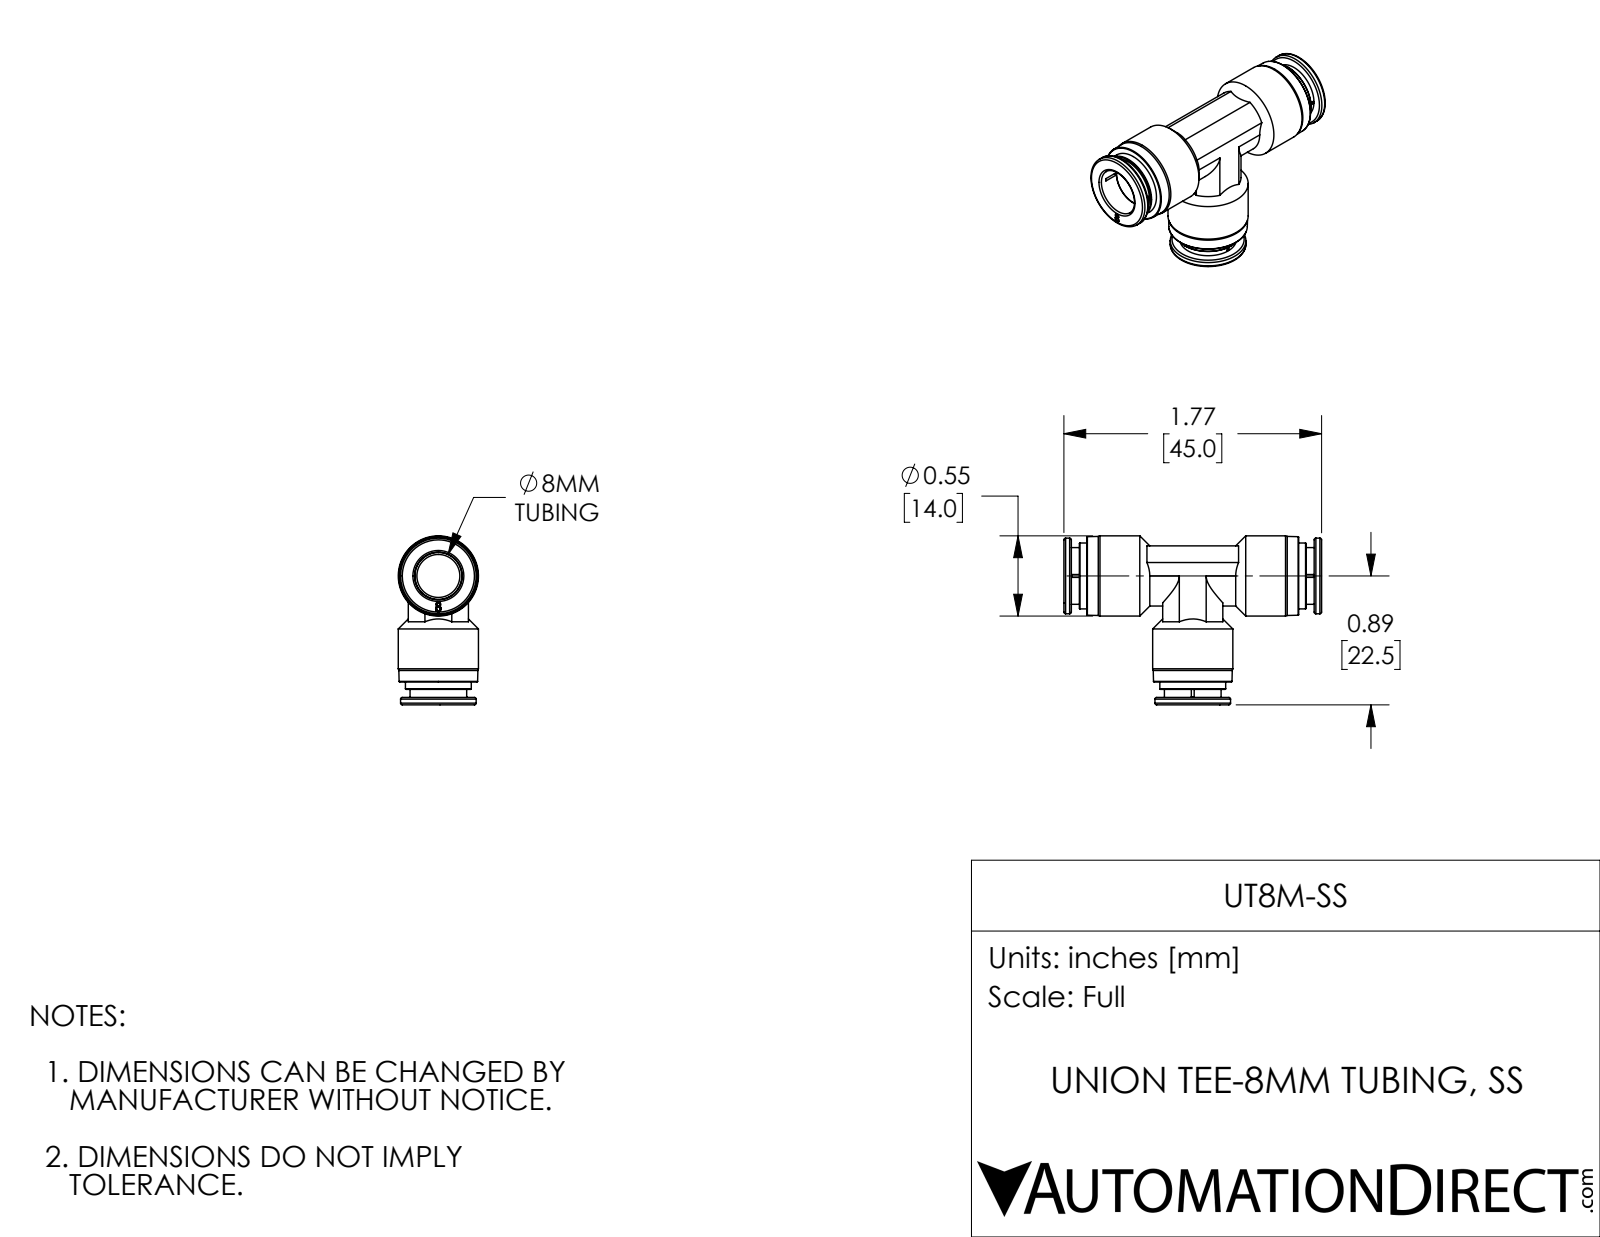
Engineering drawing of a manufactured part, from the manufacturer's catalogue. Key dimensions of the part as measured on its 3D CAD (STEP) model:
Part name (STEP PRODUCT): UT8M-SS
STEP written by: SolidWorks 2017 (AUTOMOTIVE_DESIGN)
Units: inches
Bodies: 1 solid, 201 faces (50 planar, 55 cylindrical, 96 other)
Overall size (bounding box): 1.772 × 1.161 × 0.551
Volume: 0.274 in³ · Surface area: 7.634 in²
Round holes (diameter × count): ⌀0.295 ×2, ⌀0.323 ×2, ⌀0.327 ×2, ⌀0.394 ×2
Round bosses / shafts (diameter × count): ⌀0.551 ×2, ⌀0.52 ×2, ⌀0.453 ×2, ⌀0.39 ×2
Partial cylindrical surfaces — rounded edges, fillets, slot ends (radius × count): R0.207 ×1
Main face-to-face distances: 0.051, 0.106, 0.157, 1.614, 1.72, 1.563, 1.093, 0.413, 1.041, 0.935
